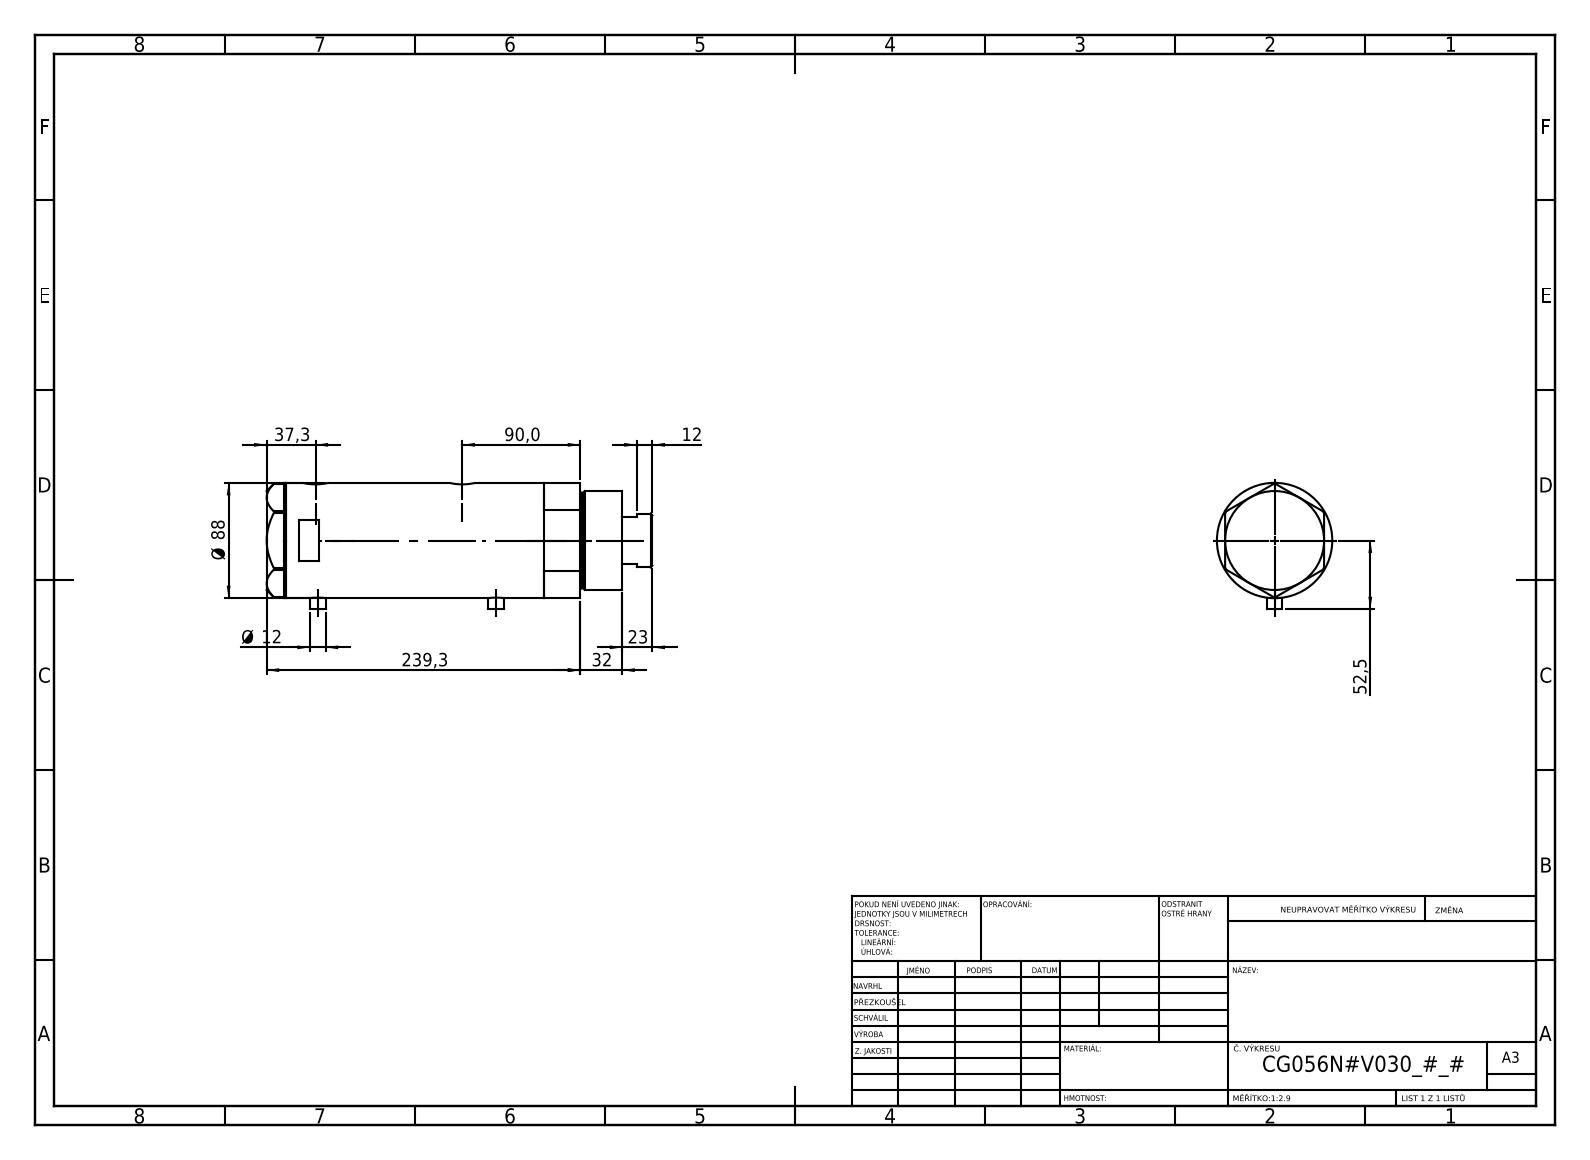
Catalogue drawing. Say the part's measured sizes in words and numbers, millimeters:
The part is named "V270CG_VC; V270CG_MIDDLE; V270CG_BACK; V270CG_FRONT". Its 3-D file was written by "SolidWorks 2019 (CONFIG_CONTROL_DESIGN)". It is 4 solids with 121 faces: 52 planar, 49 cylindrical and 20 other. Overall it measures 294.3 by 96.5 by 88 millimeters. Its volume is 1 556 000 cubic millimeters and its surface area 222 314 square millimeters. Round holes: 2 of diameter 12.5, 2 of diameter 13.16, 2 of diameter 20, 1 of diameter 14.5, 1 of diameter 42, 1 of diameter 43.5, 1 of diameter 56, 1 of diameter 60, 1 of diameter 80. Round bosses or shafts: 2 of diameter 12, 1 of diameter 88, 1 of diameter 75, 1 of diameter 73, 1 of diameter 41. The main face-to-face distances are 134.4, 26, 108.4, 15, 41, 149.4, 256.3, 271.3, 230.3, 121.9. The hole center spacings are 1.7, 25.8, 110.3, 112, 136.1, 137.8.
